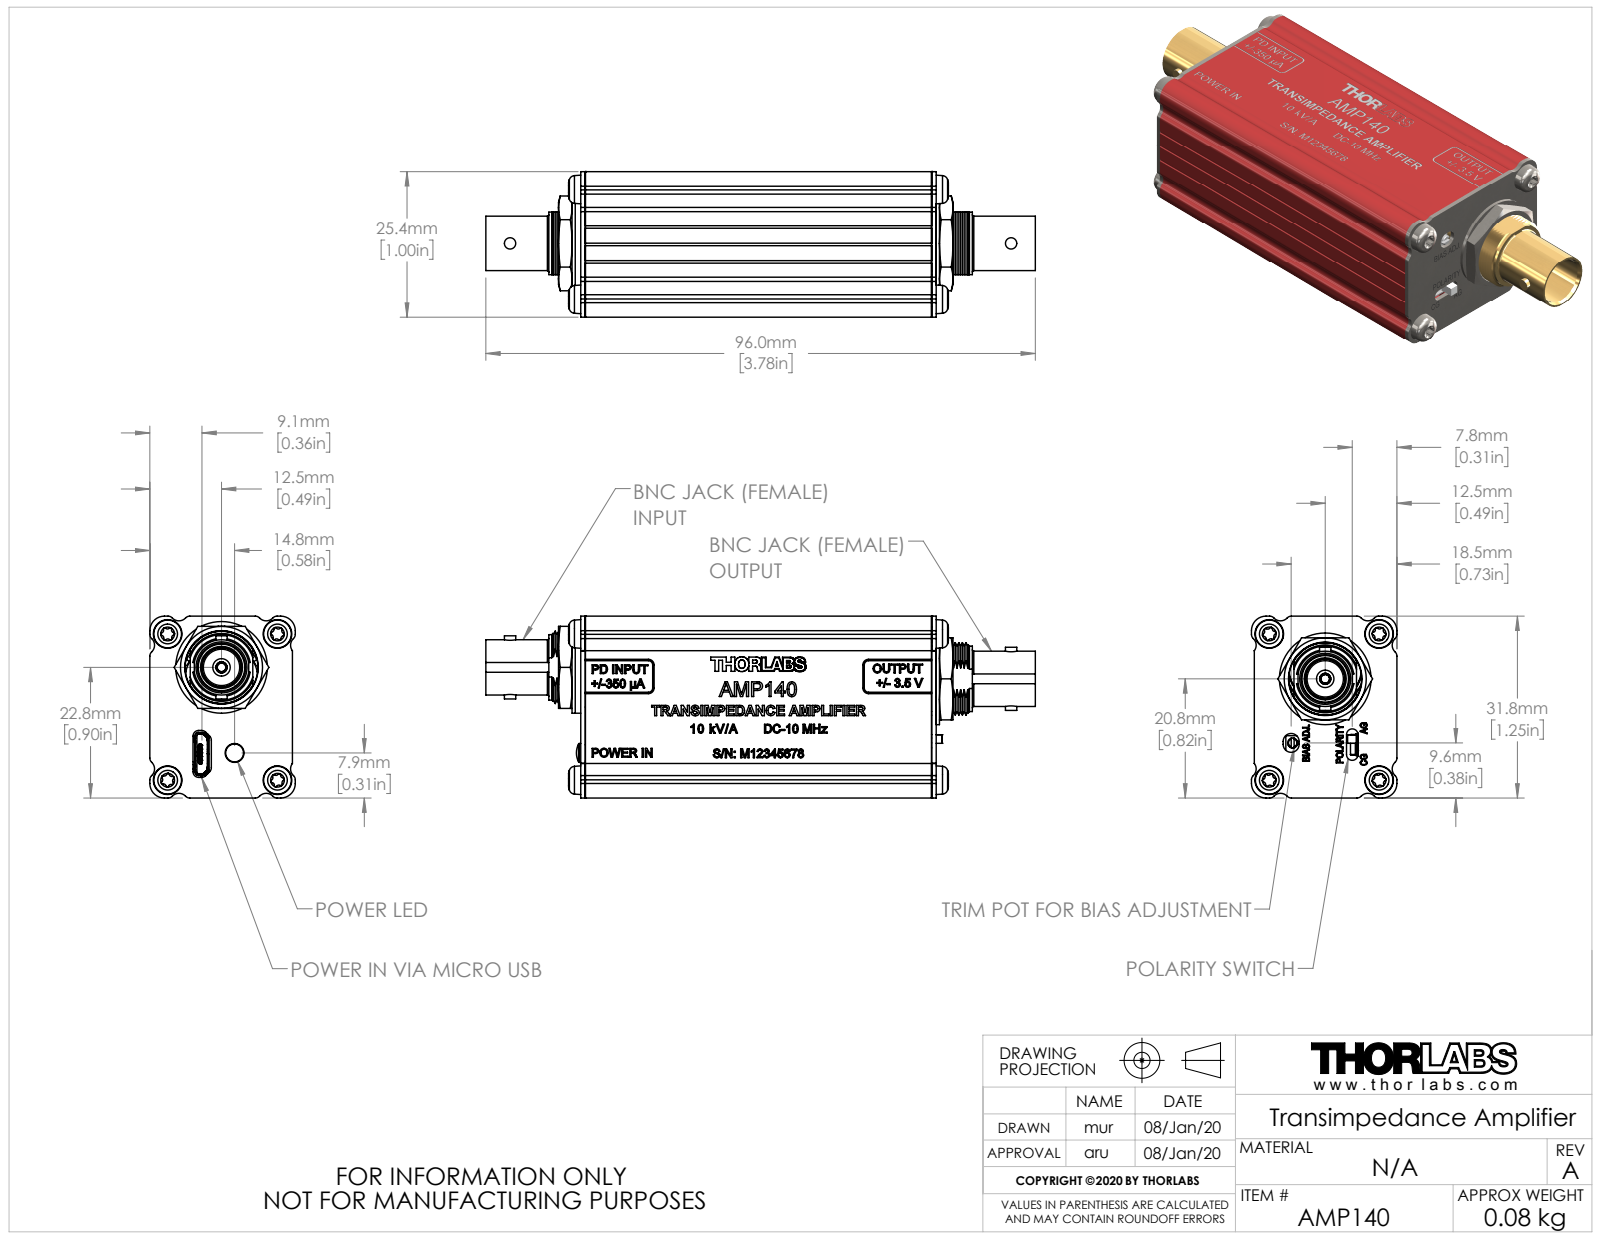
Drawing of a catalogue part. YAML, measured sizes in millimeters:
part_name: "20.07.29_AMP140 WEB"
step_written_by: "SolidWorks 2018 (AUTOMOTIVE_DESIGN)"
units: millimeters
bodies: {solids: 0, faces: 5194, planar: 3444, cylindrical: 824, other: 926}
overall_size: [95.95, 31.75, 25.4]
round_holes:
  - {diameter: 3.5, count: 6}
  - {diameter: 0.5, count: 4}
  - {diameter: 0.85, count: 2}
  - {diameter: 1.19, count: 2}
  - {diameter: 1.49, count: 2}
  - {diameter: 1.93, count: 2}
  - {diameter: 4.04, count: 2}
  - {diameter: 6.93, count: 2}
  - {diameter: 8.86, count: 2}
  - {diameter: 12.7, count: 2}
  - {diameter: 14, count: 2}
  - {diameter: 0.8, count: 1}
round_bosses_or_shafts:
  - {diameter: 0.46, count: 6}
  - {diameter: 5.3, count: 4}
  - {diameter: 2.75, count: 4}
  - {diameter: 2.5, count: 4}
  - {diameter: 2.22, count: 4}
  - {diameter: 16, count: 2}
  - {diameter: 11.43, count: 2}
  - {diameter: 10.46, count: 2}
partial_cylinders:
  - {radius: 0.1, count: 79}
  - {radius: 0.24, count: 48}
  - {radius: 0.42, count: 48}
  - {radius: 0.2, count: 30}
  - {radius: 0.5, count: 22}
  - {radius: 0.15, count: 18}
  - {radius: 1.02, count: 14}
  - {radius: 0.25, count: 12}
face_to_face_distances: [1.27, 3.05, 12, 1.64, 0.8, 9.14, 61.28, 6.1, 12.19, 4.32]
hole_center_spacings: [19.18, 2, 11.07, 11.08, 11.37, 11.38, 12.25, 12.52]
